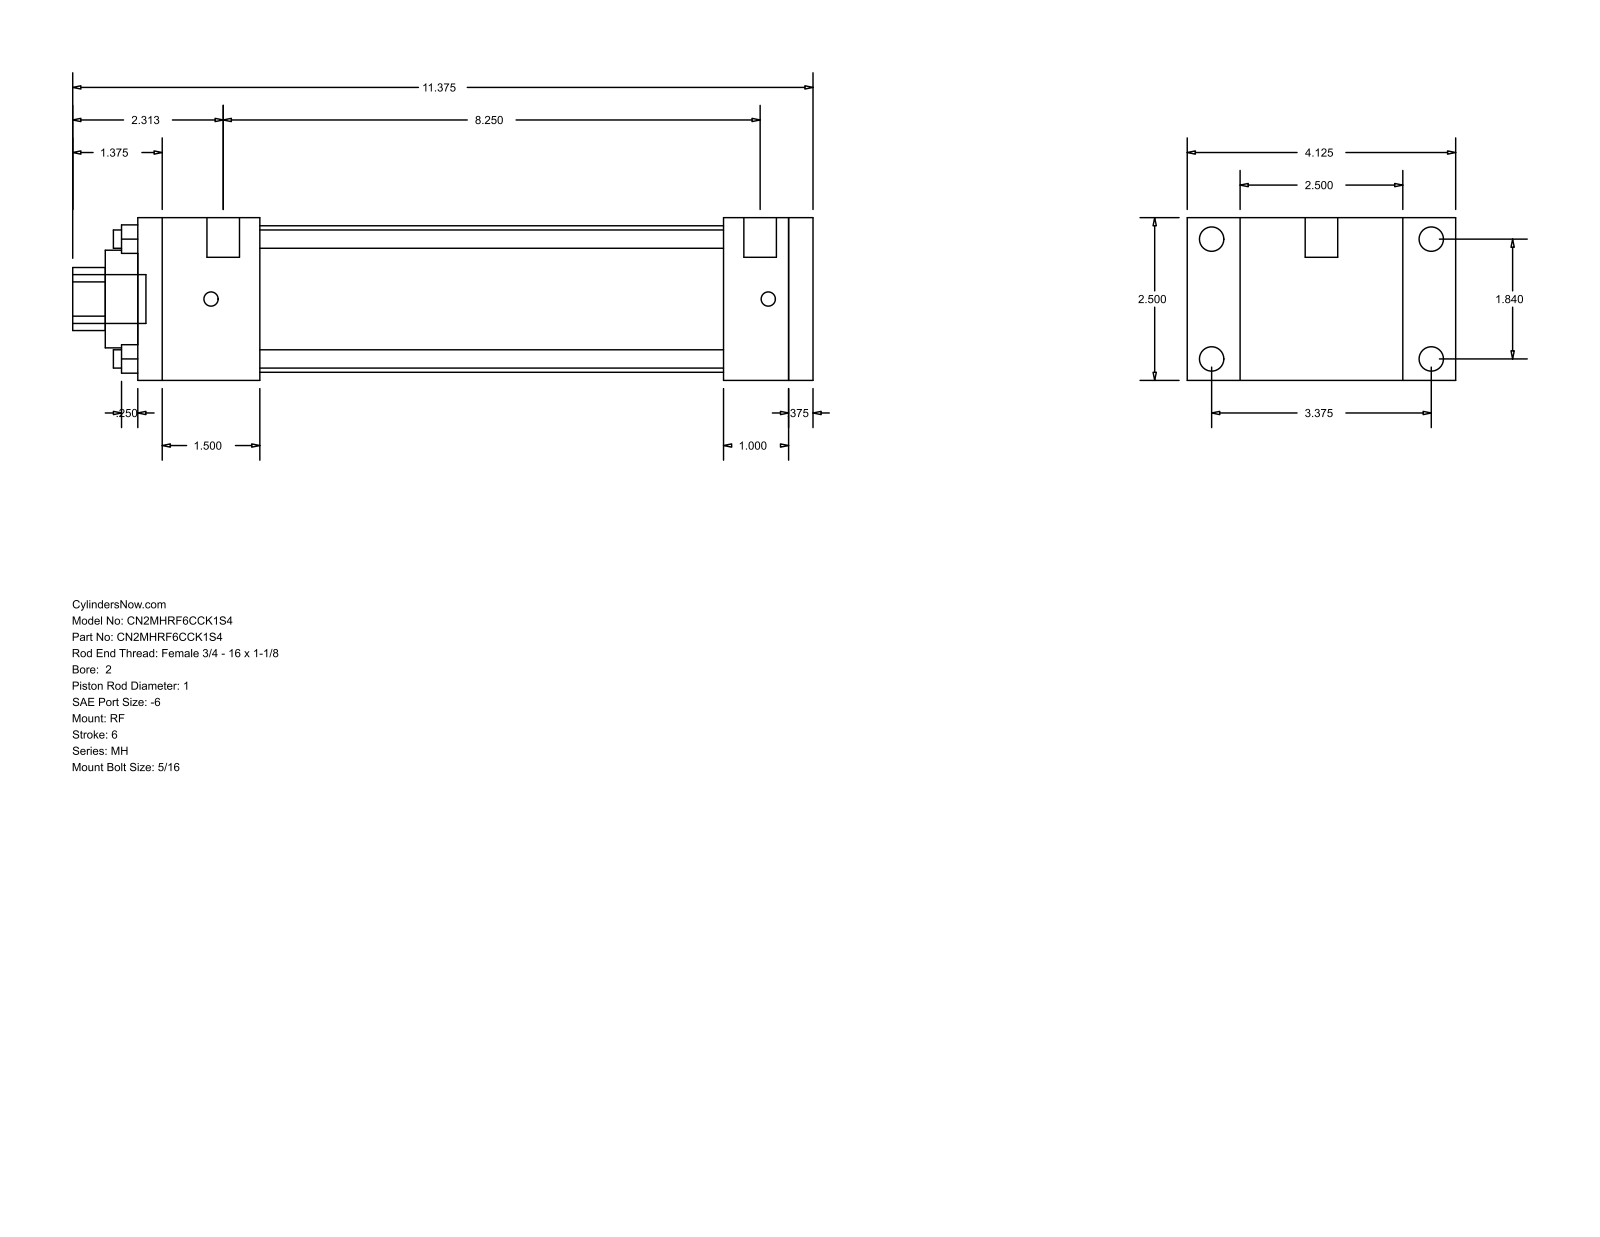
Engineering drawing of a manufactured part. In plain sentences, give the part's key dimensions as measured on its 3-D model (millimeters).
The part is named "MH_RF__0200_1". Its 3-D file was written by "GSSL Pune (CONFIG_CONTROL_DESIGN)". It is 0 solids with 92 faces: 64 planar, 28 cylindrical and 0 other. Overall it measures 288.93 by 104.78 by 63.5 millimeters. Round holes: 4 of diameter 7.14, 1 of diameter 25.4, 1 of diameter 38.1, 1 of diameter 57.15. Round bosses or shafts: 4 of diameter 9.53, 4 of diameter 5.56, 2 of diameter 12.7, 1 of diameter 19.05. Partial cylindrical surfaces (rounded edges, fillets, slot ends): 1 of radius 12.29. The main face-to-face distances are 63.5, 263.53, 254, 9.53, 20.64, 25.4, 47.63, 228.6, 180.97, 206.37. The hole center spacings are 33.05, 46.74, 66.1.
